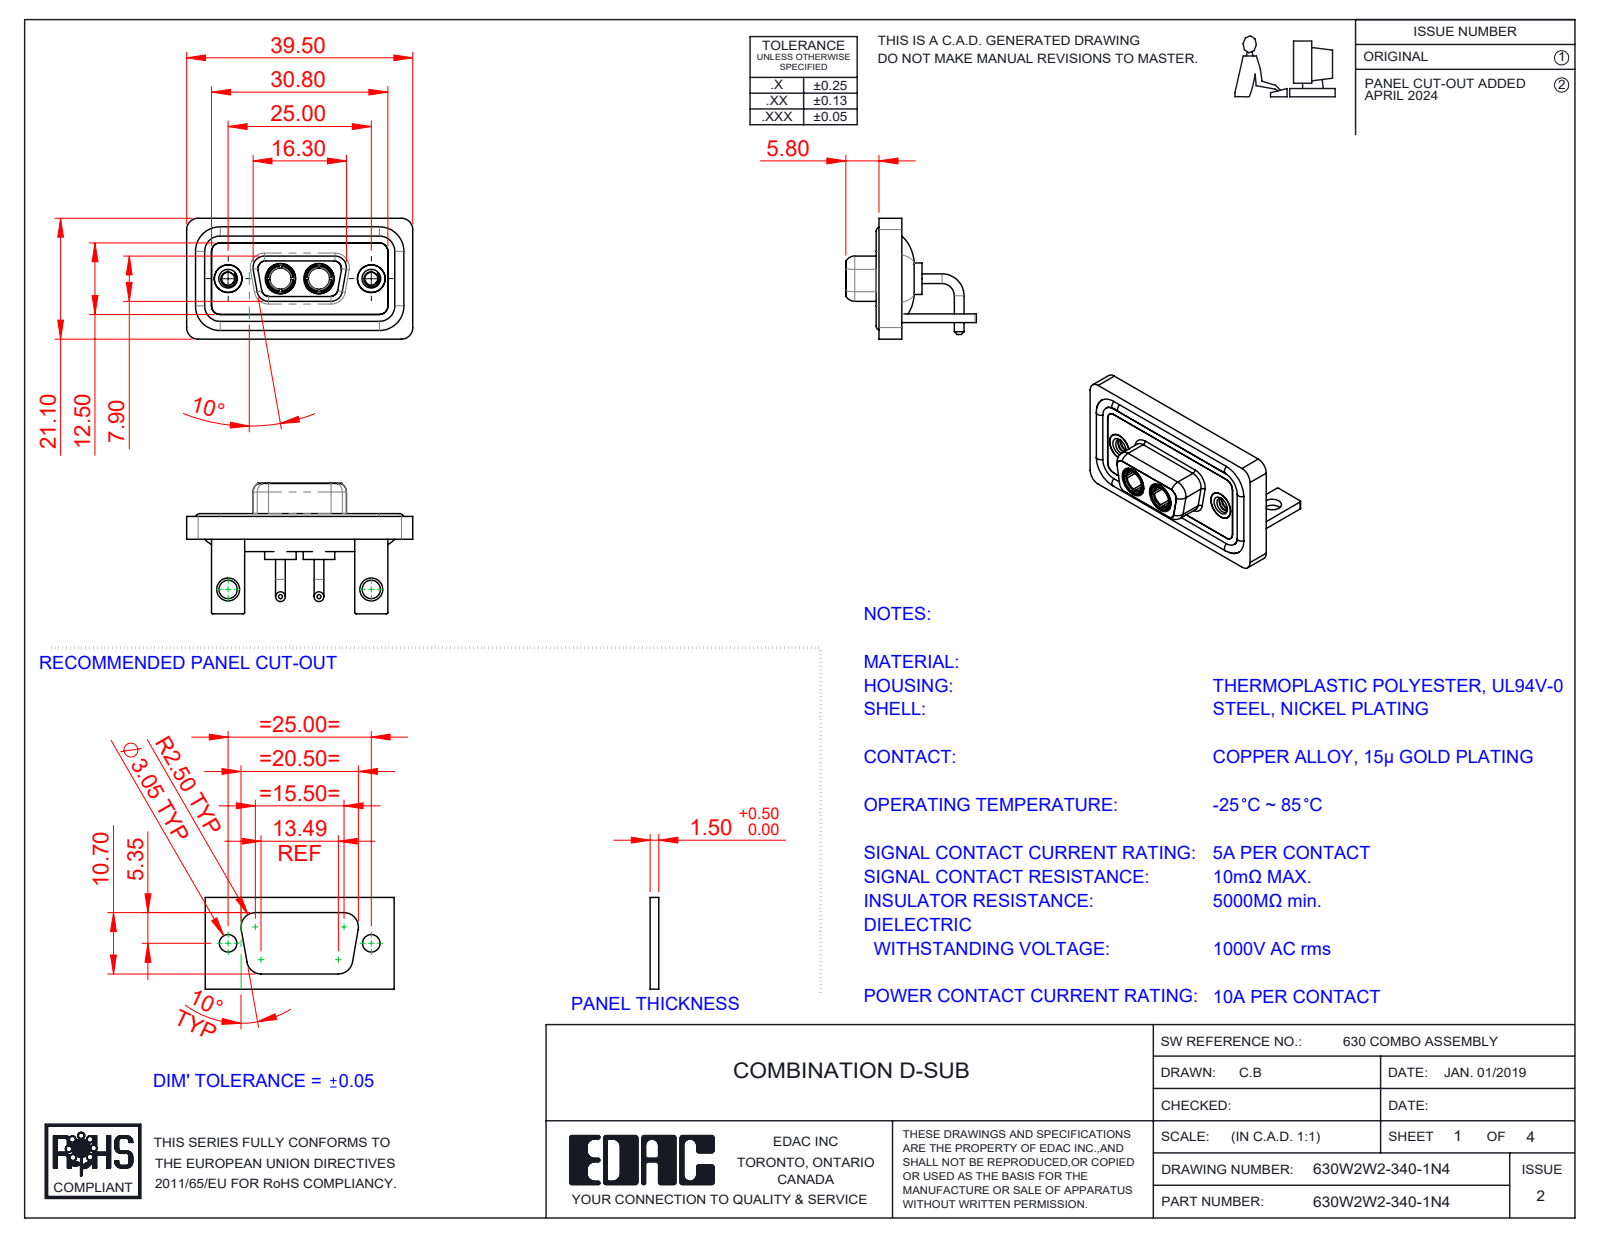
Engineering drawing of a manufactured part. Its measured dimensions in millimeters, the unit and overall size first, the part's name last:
Units: millimetres
Overall size (bounding box): 39.5 × 22.8 × 21.1
Round holes (diameter × count): ⌀4.85 ×4, ⌀2.26 ×2, ⌀3.2 ×2, ⌀3.7 ×2, ⌀4 ×2, ⌀4.05 ×2, ⌀5 ×2, ⌀5.3 ×2
Round bosses / shafts (diameter × count): ⌀1.7 ×4, ⌀1.6 ×4, ⌀5.5 ×2, ⌀5.2 ×2, ⌀4.96 ×2, ⌀4.95 ×2, ⌀4.8 ×2, ⌀4.75 ×2
Partial cylindrical surfaces — rounded edges, fillets, slot ends (radius × count): R2 ×19, R1.5 ×18, R0.25 ×16, R1.35 ×8, R1.6 ×8, R0.5 ×5, R0.6 ×4, R0.65 ×4
Main face-to-face distances: 0.4, 2.9, 1.5, 1.8, 1.1, 3.7, 0.8, 2.5, 1.6, 3.1
Hole centre spacings: 9.14, 15.86, 25, 6.72
Volume: 5 067 mm³ · Surface area: 8 420 mm²
Bodies: 13 solids, 590 faces (183 planar, 262 cylindrical, 145 other)
Part name (STEP PRODUCT): 630Combo Waterproof Housing_09 Contacts; 630Combo Housing_2W2; 630Combo Shell Front_09 Contacts; 630Combo Stabilizer Bracket_50 Contacts (+4 more)
STEP written by: SolidWorks 2023 (CONFIG_CONTROL_DESIGN)
